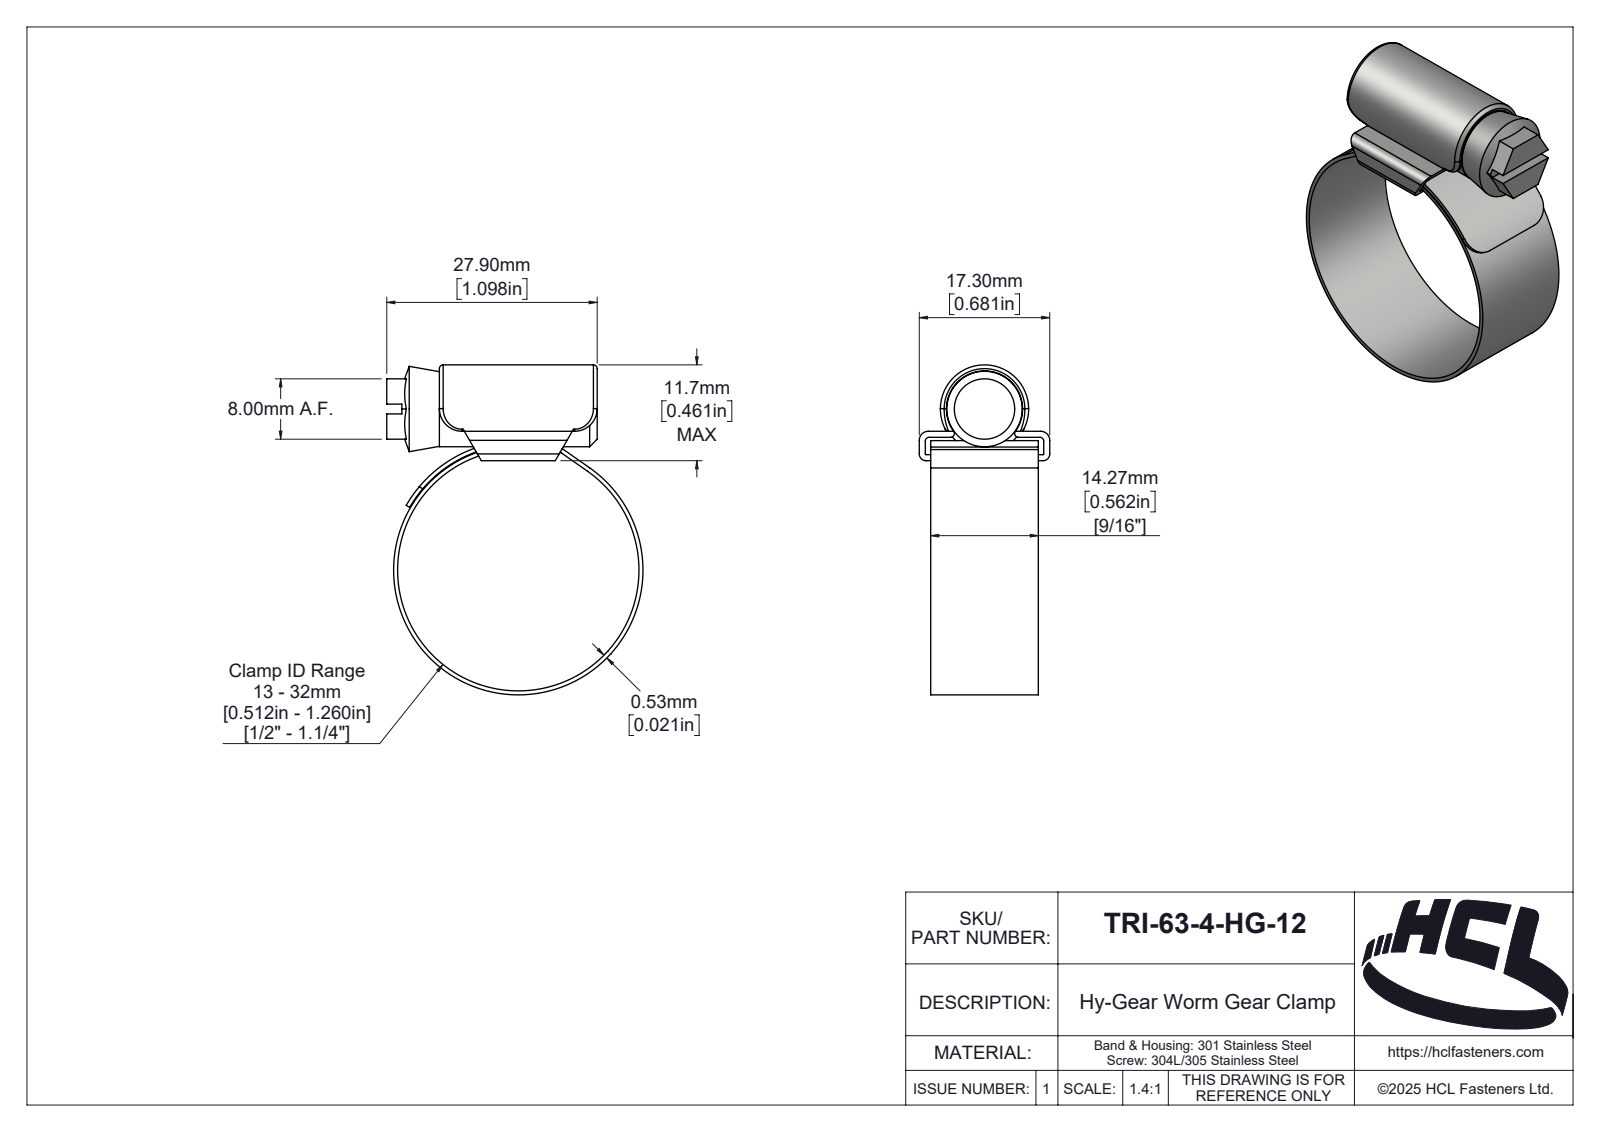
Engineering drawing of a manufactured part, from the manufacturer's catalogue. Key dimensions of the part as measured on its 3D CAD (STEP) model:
Part name (STEP PRODUCT): TRI-50-0-HG-12
STEP written by: SolidWorks 2025 (AUTOMOTIVE_DESIGN)
Units: millimetres
Bodies: 3 solids, 189 faces (39 planar, 89 cylindrical, 61 other)
Overall size (bounding box): 43.73 × 33.97 × 17.3
Volume: 3 699 mm³ · Surface area: 6 357 mm²
Round holes (diameter × count): ⌀32 ×1
Round bosses / shafts (diameter × count): ⌀33.06 ×1, ⌀10 ×1
Partial cylindrical surfaces — rounded edges, fillets, slot ends (radius × count): R0.5 ×6, R3 ×4, R0.1 ×2, R0.9 ×2, R1.2 ×2, R0.46 ×1, R1.89 ×1, R2 ×1
Main face-to-face distances: 0.8, 3.1, 2.3, 3.9, 14.26, 0.53, 27.9, 1.52, 15.78, 16.5
